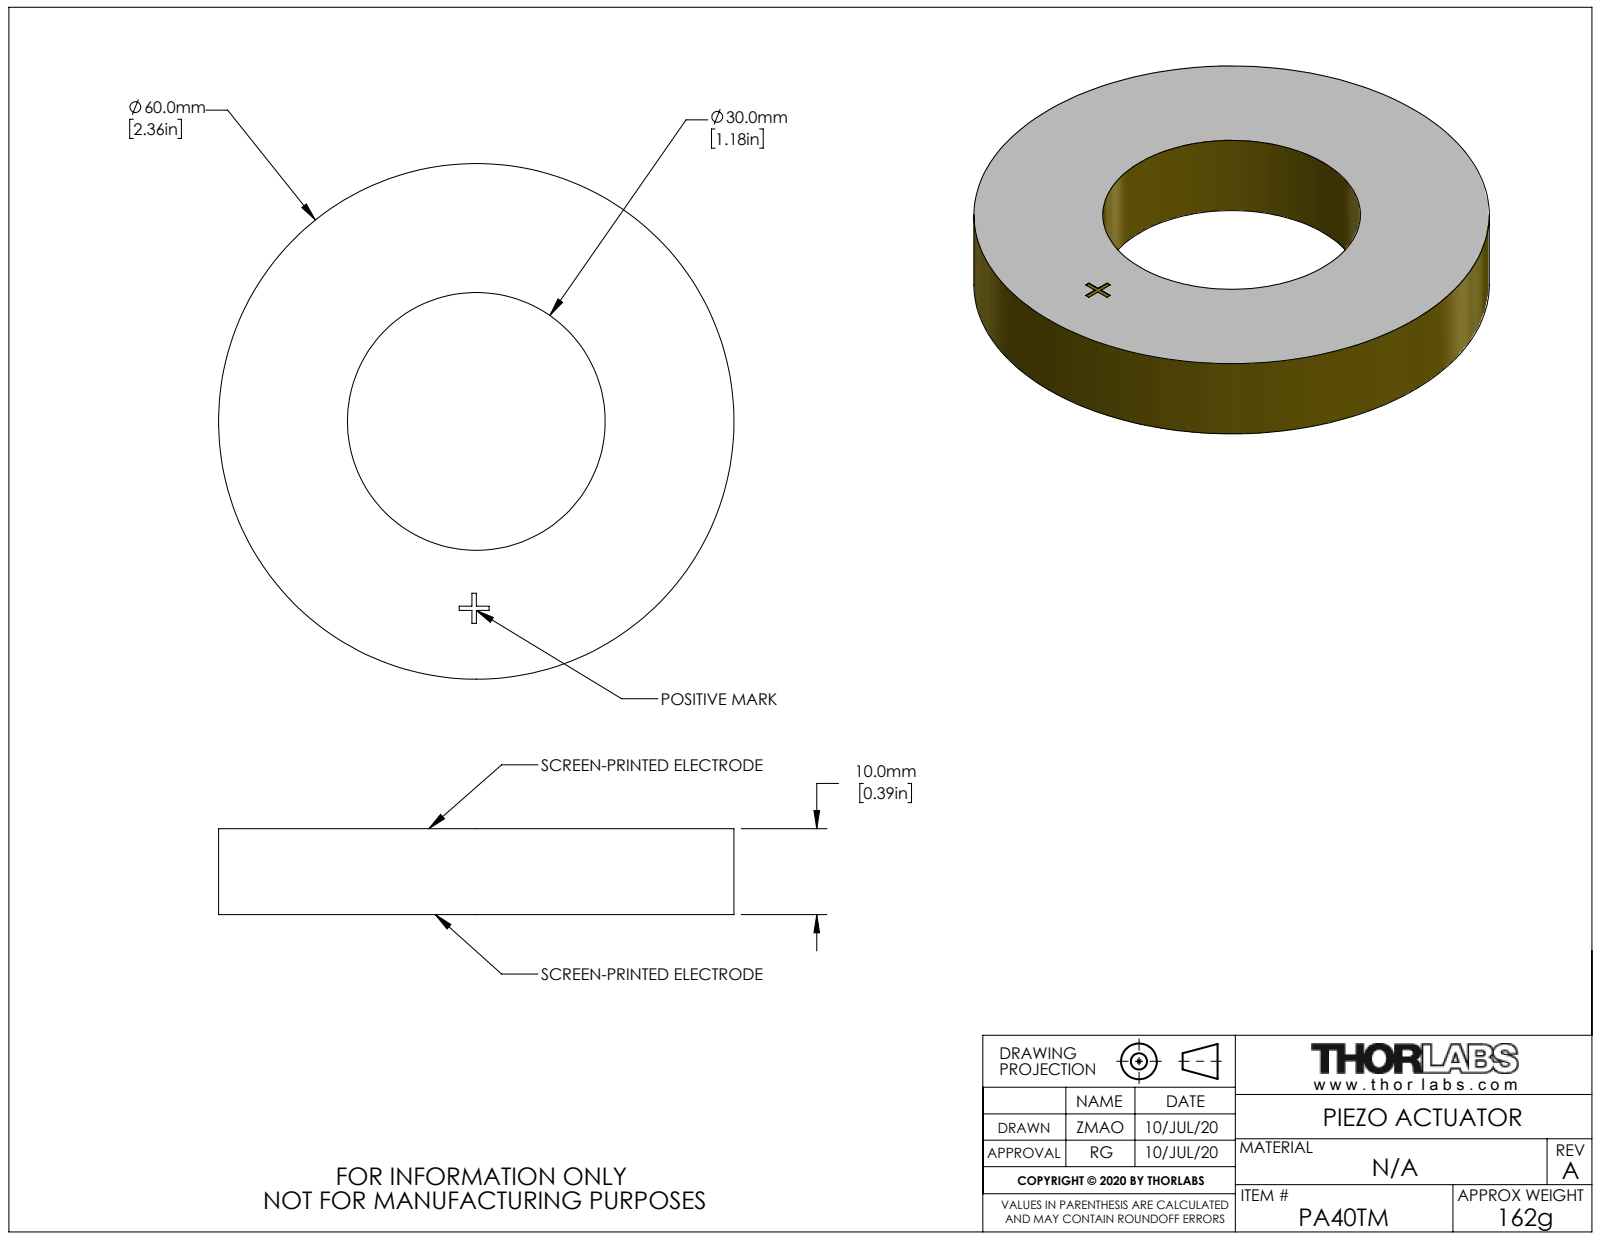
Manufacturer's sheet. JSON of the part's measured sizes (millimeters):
{"part_name": "CTN016247-E0W", "step_written_by": "SolidWorks 2018 (AUTOMOTIVE_DESIGN)", "units": "millimeters", "bodies": {"solids": 1, "faces": 19, "planar": 15, "cylindrical": 4, "other": 0}, "overall_size": [60, 60, 10], "volume_mm3": 21206, "surface_area_mm2": 7069, "round_holes": [[30, 1]], "round_bosses_or_shafts": [[60, 1]], "face_to_face_distances": [10, 9.99, 0.5, 1.5, 2, 3.5]}
